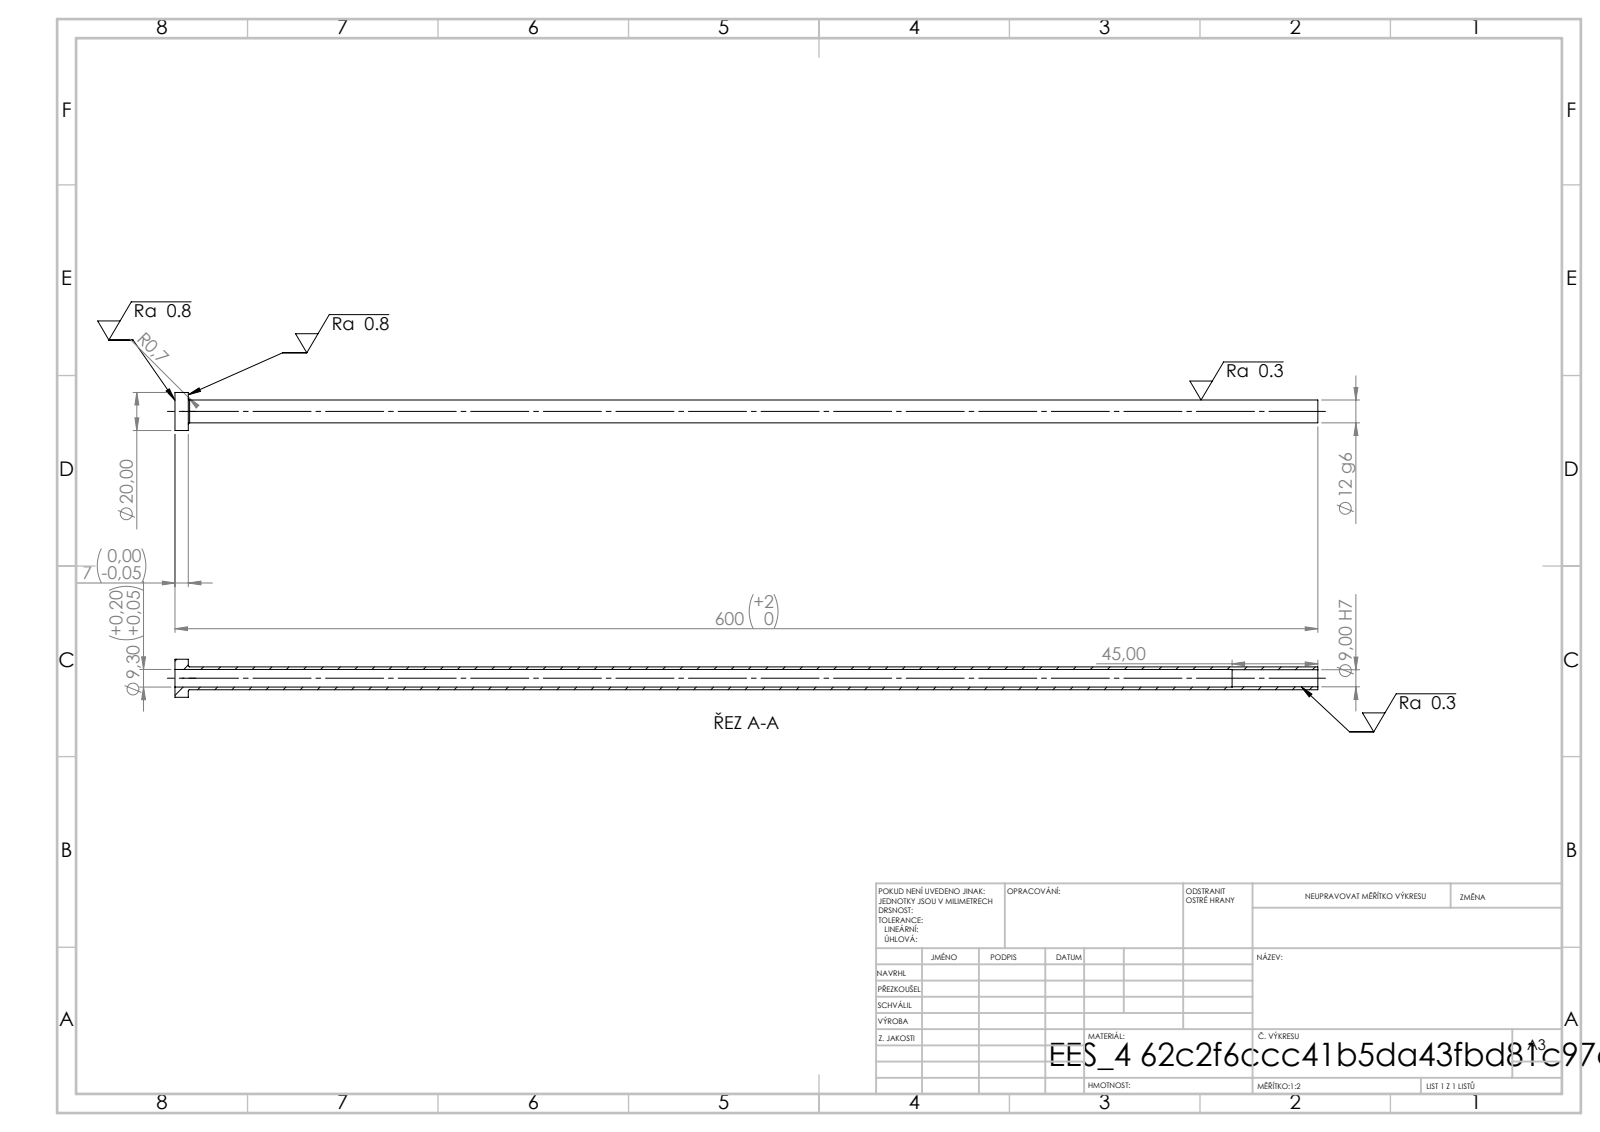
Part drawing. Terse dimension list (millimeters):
written by: SolidWorks 2019 (CONFIG_CONTROL_DESIGN)
unit: mm
bodies: 1 solid, 14 faces (4 planar, 8 cylindrical, 2 other)
size: 600 × 20 × 20
volume: 28 706 mm³; area: 40 773 mm²
holes: 1× ⌀9, 1× ⌀9.3
bosses: 1× ⌀20, 1× ⌀12
face distances: 7, 600, 593, 555, 548, 45
